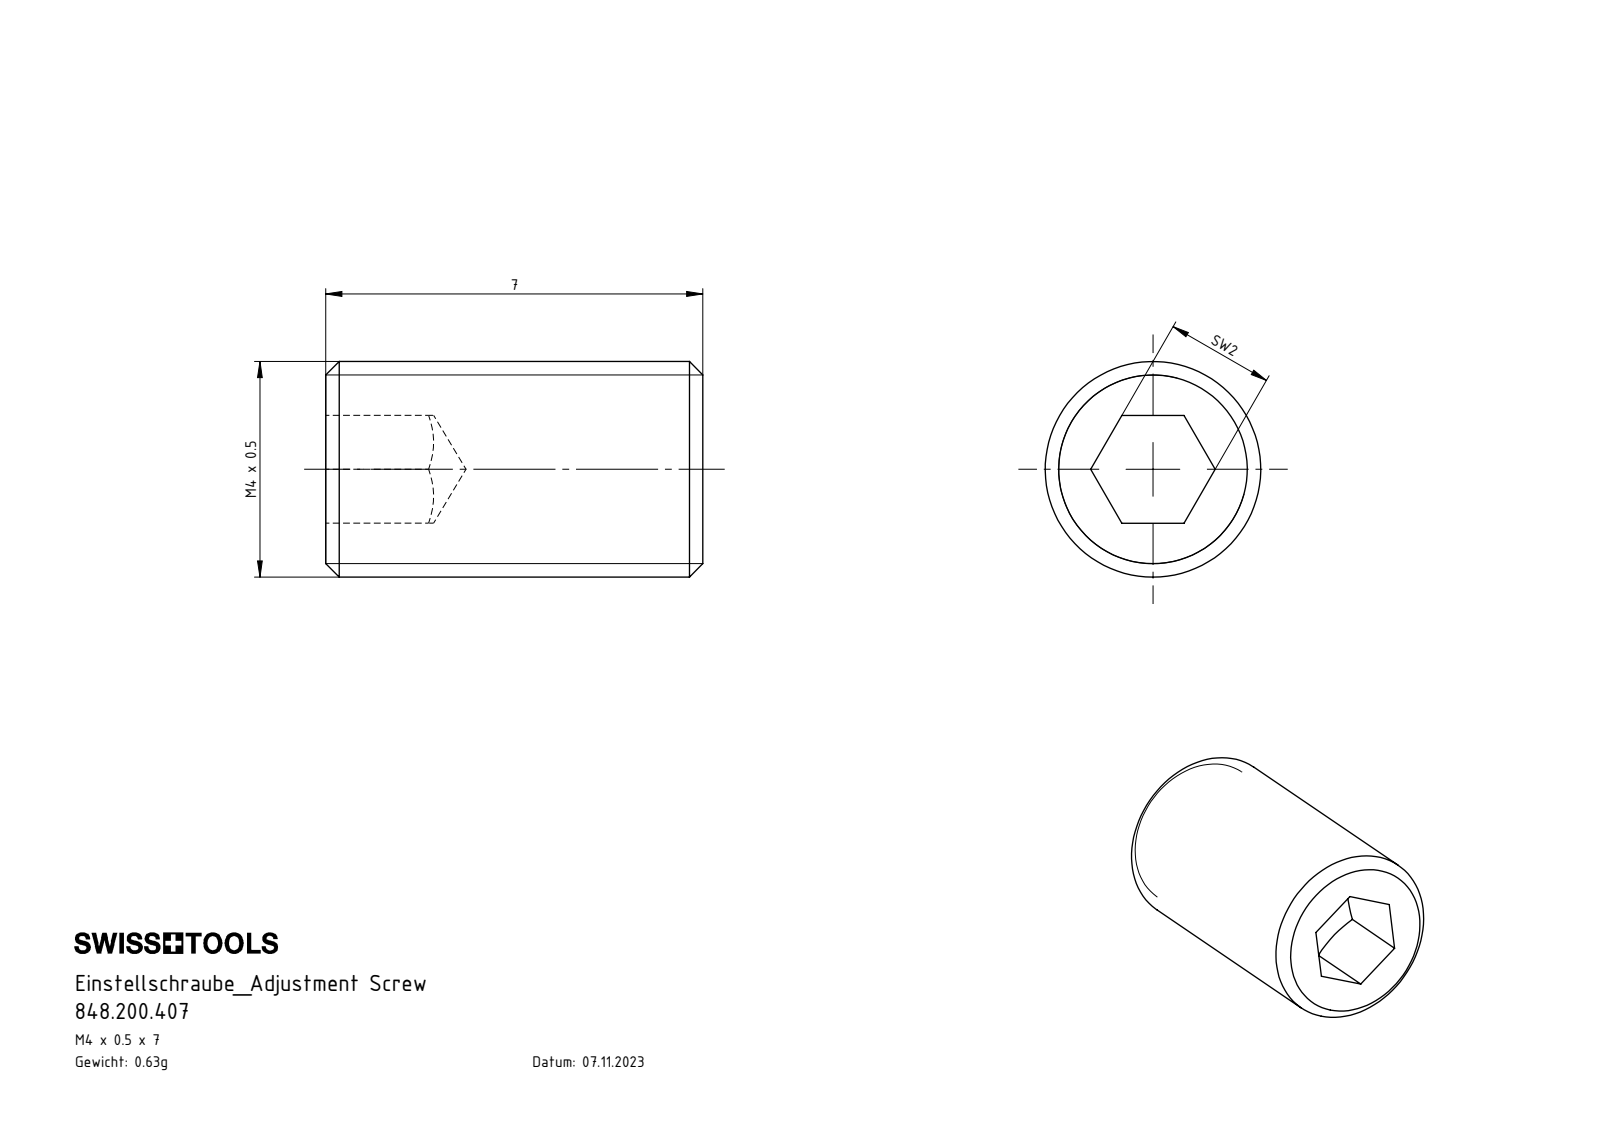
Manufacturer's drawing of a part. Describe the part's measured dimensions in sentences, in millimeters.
The part is named "848.200.407". Its 3-D file was written by "SolidWorks 2022 (AUTOMOTIVE_DESIGN)". It is 1 solid with 16 faces: 8 planar, 2 cylindrical and 6 other. Overall it measures 7 by 4 by 4 millimeters. Its volume is 80 cubic millimeters and its surface area 123 square millimeters. Round bosses or shafts: 1 of diameter 4. The main face-to-face distances are 2, 7.
